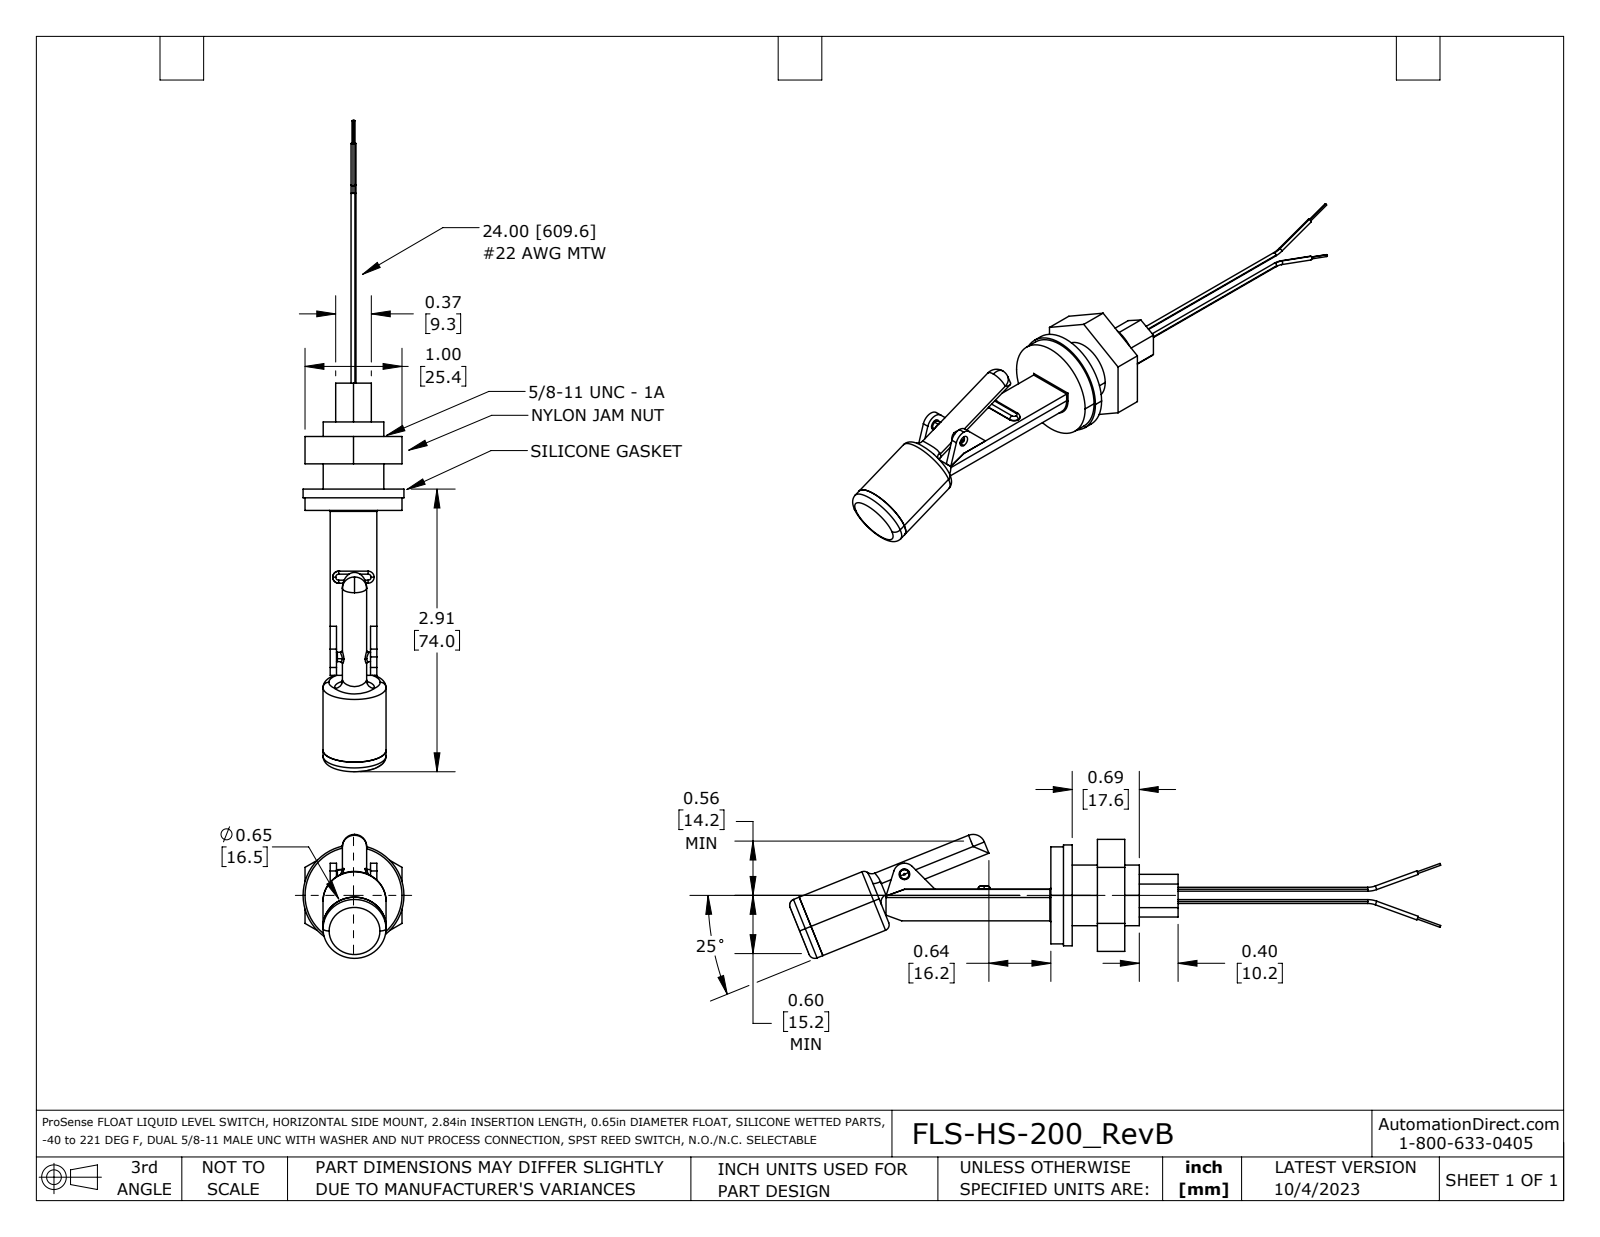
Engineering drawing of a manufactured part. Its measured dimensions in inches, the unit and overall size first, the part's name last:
Units: inches
Overall size (bounding box): 6.714 × 1.278 × 1.04
Round holes (diameter × count): ⌀0.01 ×1, ⌀0.11 ×1, ⌀0.45 ×1, ⌀0.5 ×1, ⌀0.53 ×1, ⌀0.56 ×1, ⌀0.62 ×1, ⌀0.625 ×1
Round bosses / shafts (diameter × count): ⌀0.04 ×4, ⌀0.65 ×2, ⌀0.02 ×2, ⌀1.04 ×1, ⌀1 ×1, ⌀0.55 ×1, ⌀0.25 ×1, ⌀0.125 ×1
Partial cylindrical surfaces — rounded edges, fillets, slot ends (radius × count): R0.01 ×3, R0.031 ×2, R0.062 ×2, R0.18 ×2, R0.114 ×1, R0.125 ×1, R0.223 ×1, R0.241 ×1
Main face-to-face distances: 0.13, 0.35, 0.48, 0.282, 0.632, 0.762, 0.542, 0.26, 0.09, 0.22
Hole centre spacings: 0.064
Volume: 0.989 in³ · Surface area: 20.1 in²
Bodies: 11 solids, 201 faces (67 planar, 74 cylindrical, 60 other)
Part name (STEP PRODUCT): M8790_FLS-HS-200 nc coord sr1
STEP written by: SolidWorks 2021 (AUTOMOTIVE_DESIGN)
